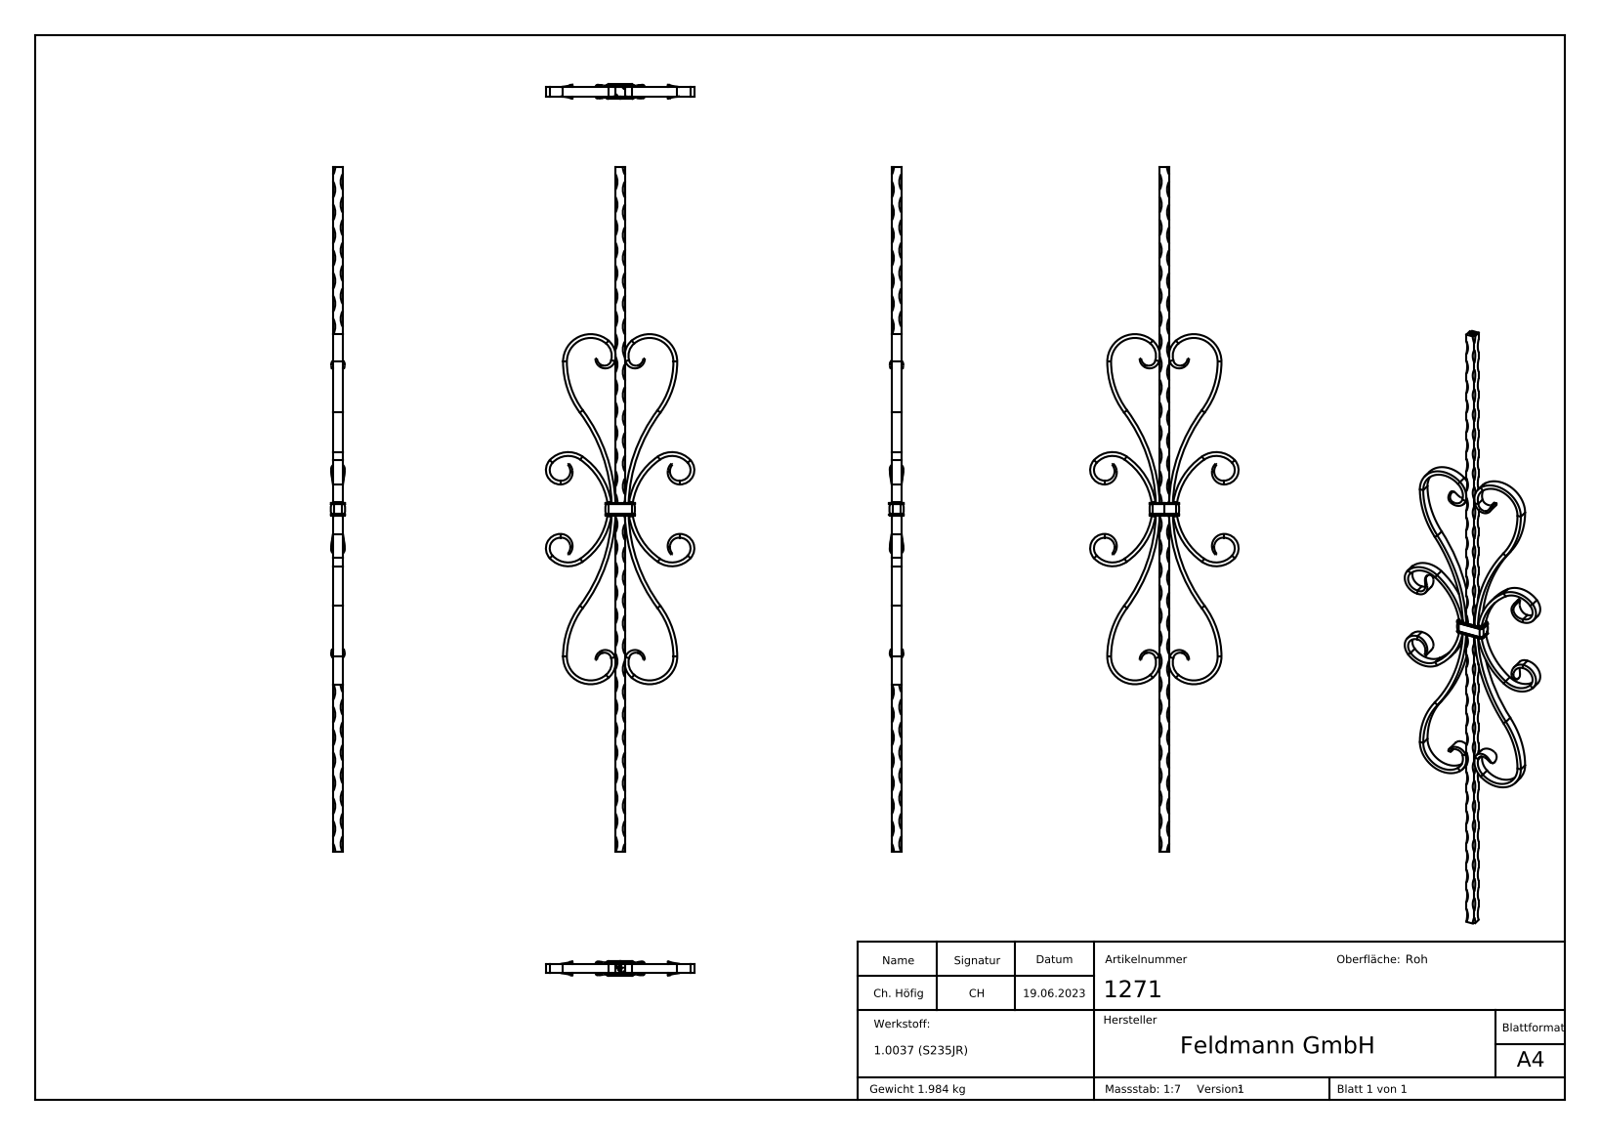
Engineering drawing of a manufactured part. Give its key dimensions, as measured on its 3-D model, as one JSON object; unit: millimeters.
{"part_name": "1271", "step_written_by": "SolidWorks 2018 (CONFIG_CONTROL_DESIGN)", "units": "millimeters", "bodies": {"solids": 4, "faces": 634, "planar": 237, "cylindrical": 117, "other": 280}, "overall_size": [900, 195, 19], "volume_mm3": 254383, "surface_area_mm2": 119799, "partial_cylinders_radius": [[0.5, 24], [0.2, 8], [1, 4], [4, 4], [14, 4], [19, 4], [21, 4], [21.62, 4]], "face_to_face_distances": [12, 0.5, 12.5, 13, 10.5, 22.5, 442, 458, 16, 33]}
